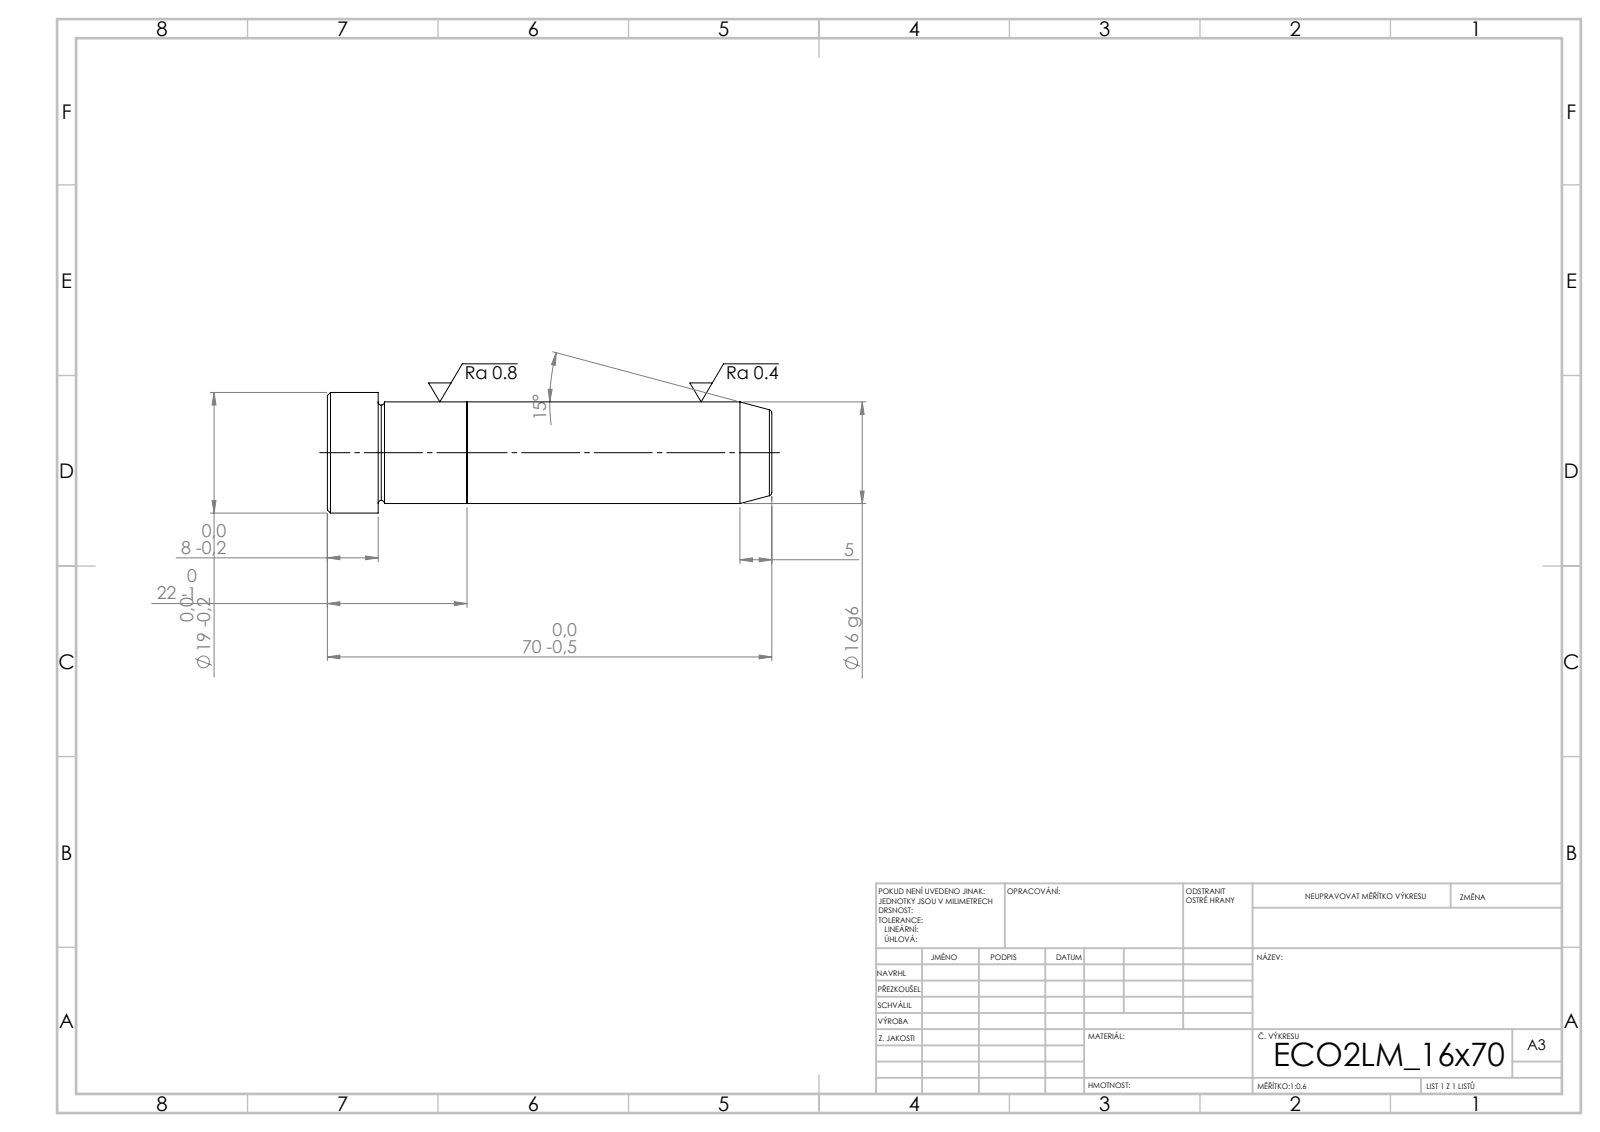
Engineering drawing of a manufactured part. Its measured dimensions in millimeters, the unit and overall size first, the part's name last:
Units: millimetres
Overall size (bounding box): 70 × 19 × 19
Round bosses / shafts (diameter × count): ⌀19 ×1, ⌀16 ×1
Main face-to-face distances: 22, 48, 70, 62, 14, 8
Volume: 14 547 mm³ · Surface area: 4 491 mm²
Bodies: 2 solids, 21 faces (5 planar, 6 cylindrical, 10 other)
STEP written by: SolidWorks 2019 (CONFIG_CONTROL_DESIGN)
